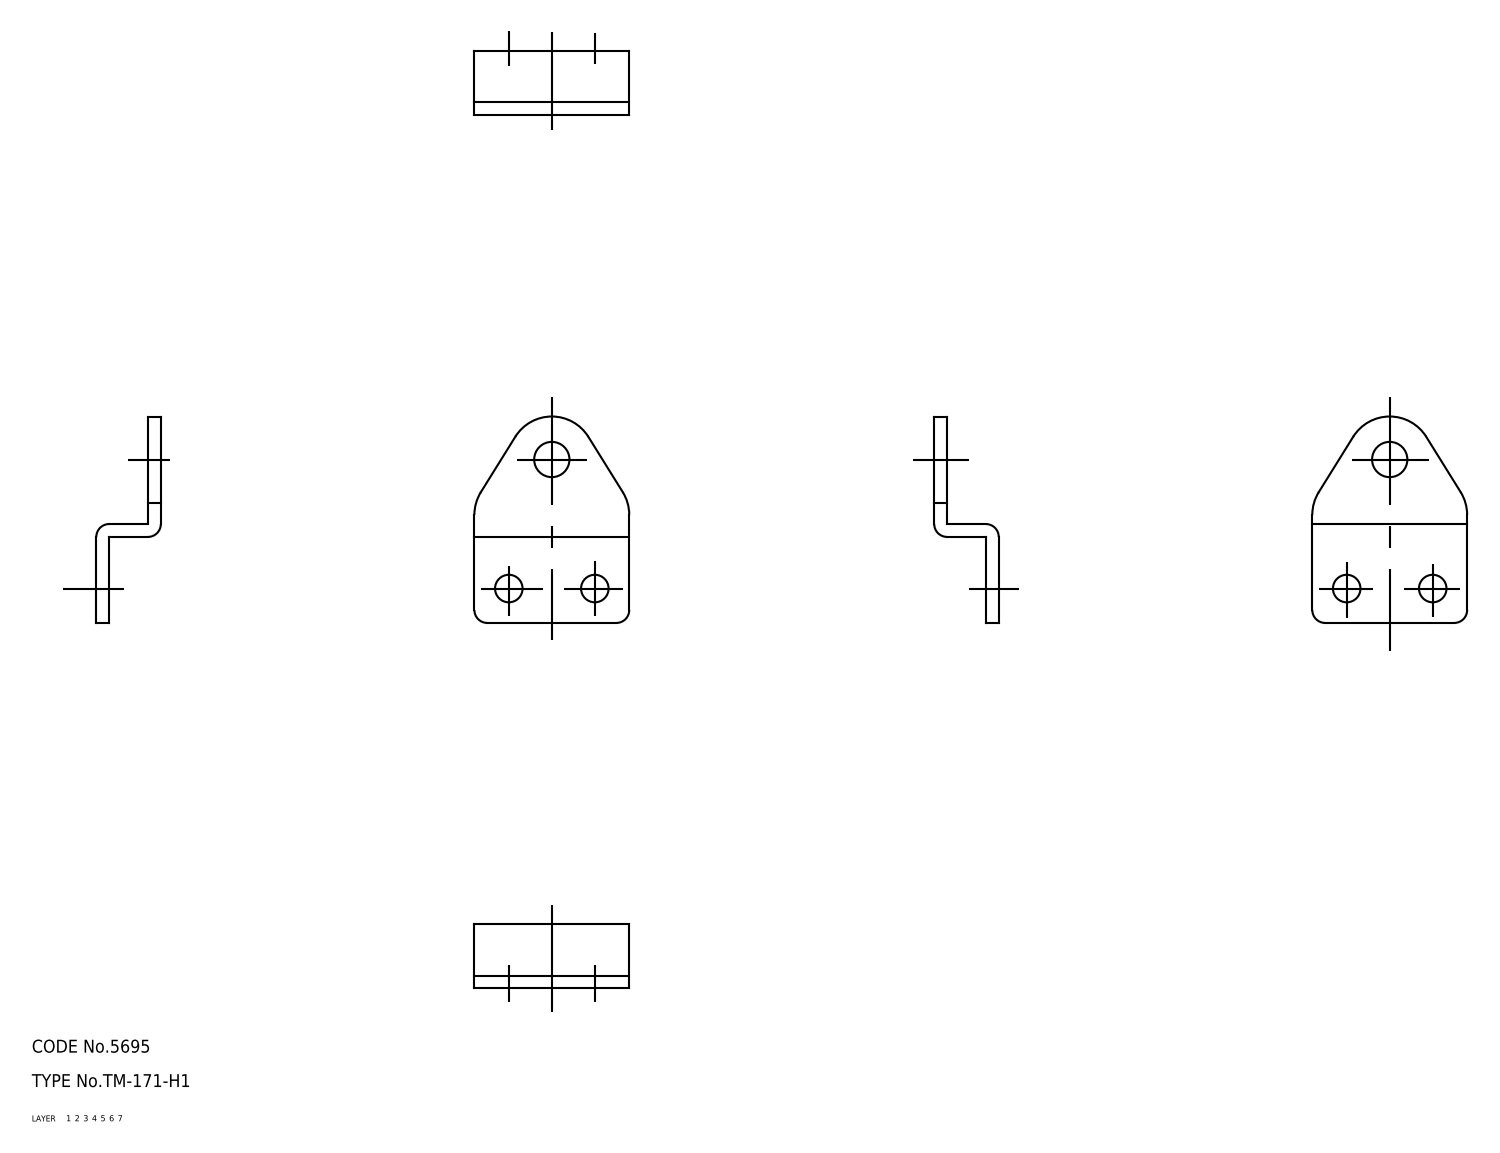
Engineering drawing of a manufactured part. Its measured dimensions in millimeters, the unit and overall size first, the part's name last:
Units: millimetres
Overall size (bounding box): 48 × 36 × 15
Volume: 5 197 mm³ · Surface area: 4 164 mm²
Bodies: 1 solid, 24 faces (0 planar, 0 cylindrical, 24 other)
Part name (STEP PRODUCT): bracket
STEP written by: CADfix (AUTOMOTIVE_DESIGN)
